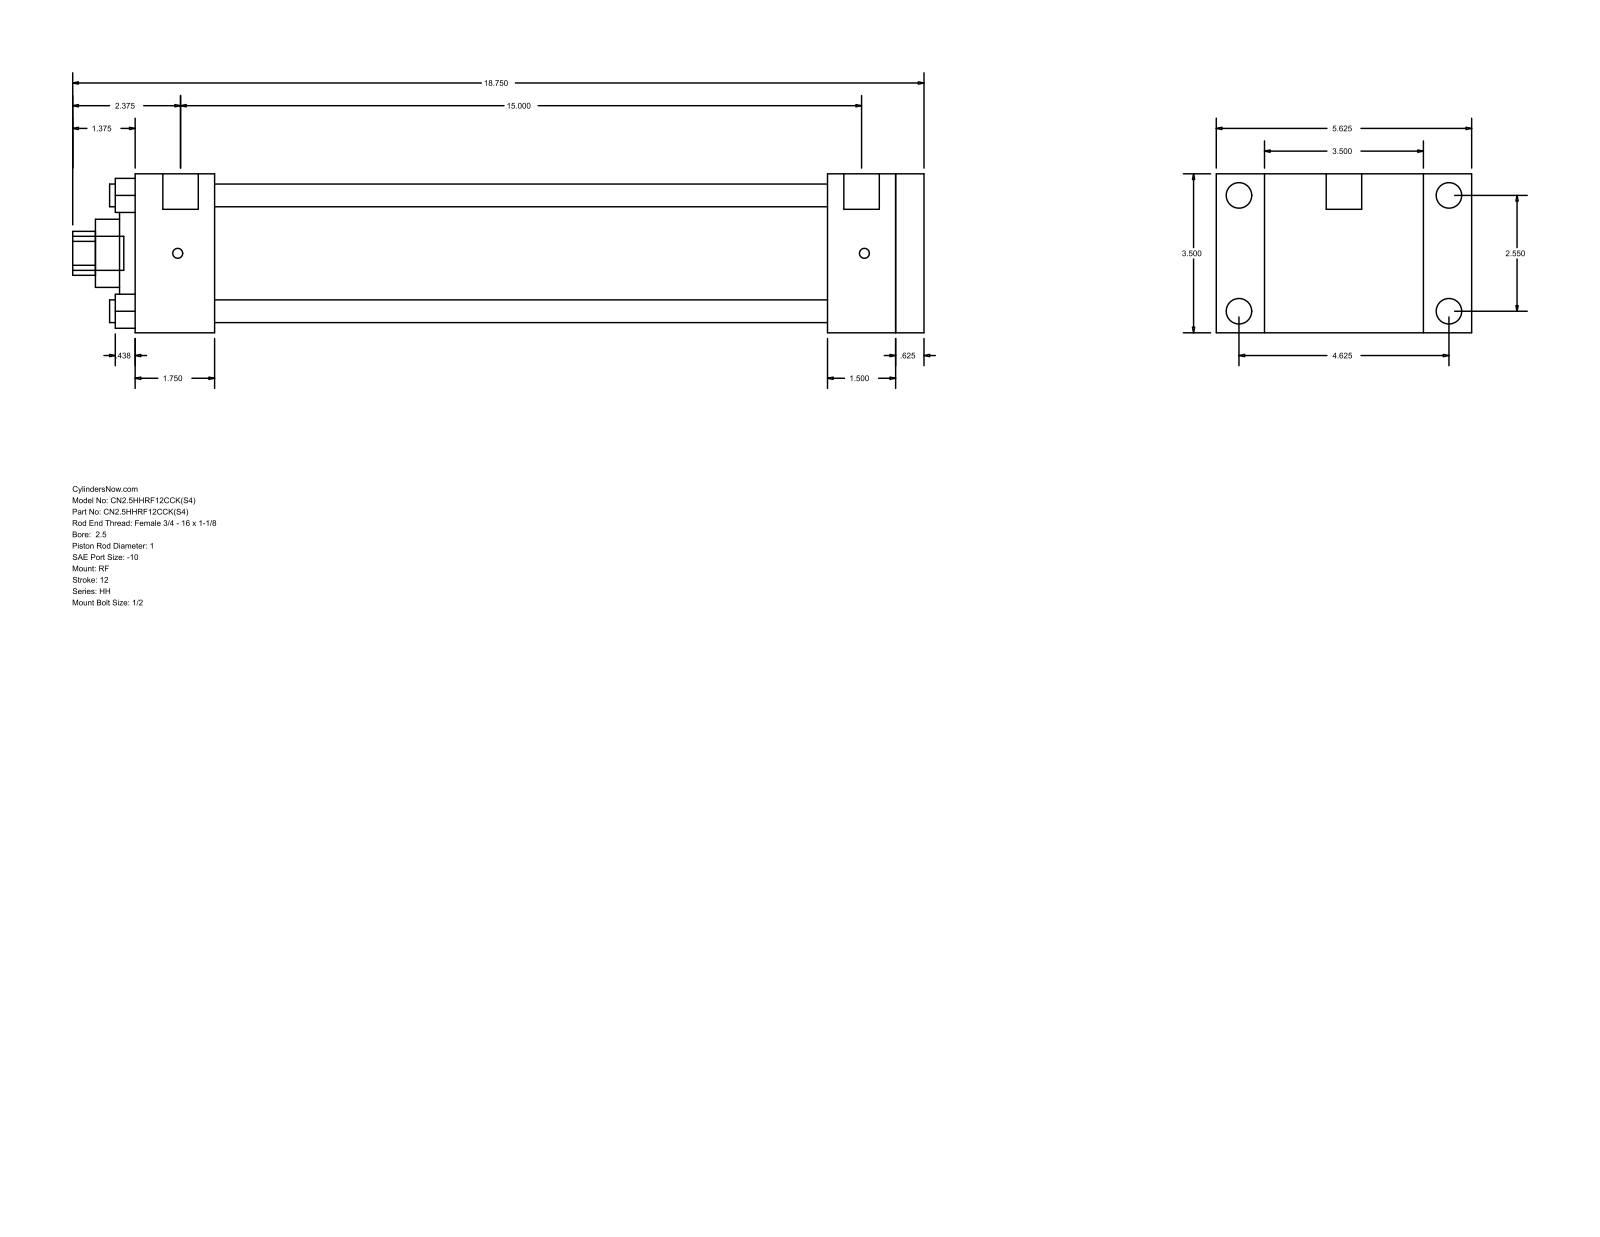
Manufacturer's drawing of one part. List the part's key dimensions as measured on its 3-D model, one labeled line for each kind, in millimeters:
Part name (STEP PRODUCT): HH_RF__0250_1
STEP written by: GSSL Pune (CONFIG_CONTROL_DESIGN)
Units: millimetres
Bodies: 0 solids, 94 faces (65 planar, 29 cylindrical, 0 other)
Overall size (bounding box): 476.25 × 142.88 × 88.9
Round holes (diameter × count): ⌀12.7 ×4, ⌀25.4 ×1, ⌀38.1 ×1, ⌀60.33 ×1, ⌀73.03 ×1
Round bosses / shafts (diameter × count): ⌀14.3 ×4, ⌀5.56 ×4, ⌀19.84 ×2, ⌀19.05 ×1
Partial cylindrical surfaces — rounded edges, fillets, slot ends (radius × count): R12.29 ×1
Main face-to-face distances: 88.9, 15.87, 425.46, 441.33, 44.46, 381, 396.87, 387.35, 342.89, 38.11
Hole centre spacings: 45.79, 64.76, 91.58
